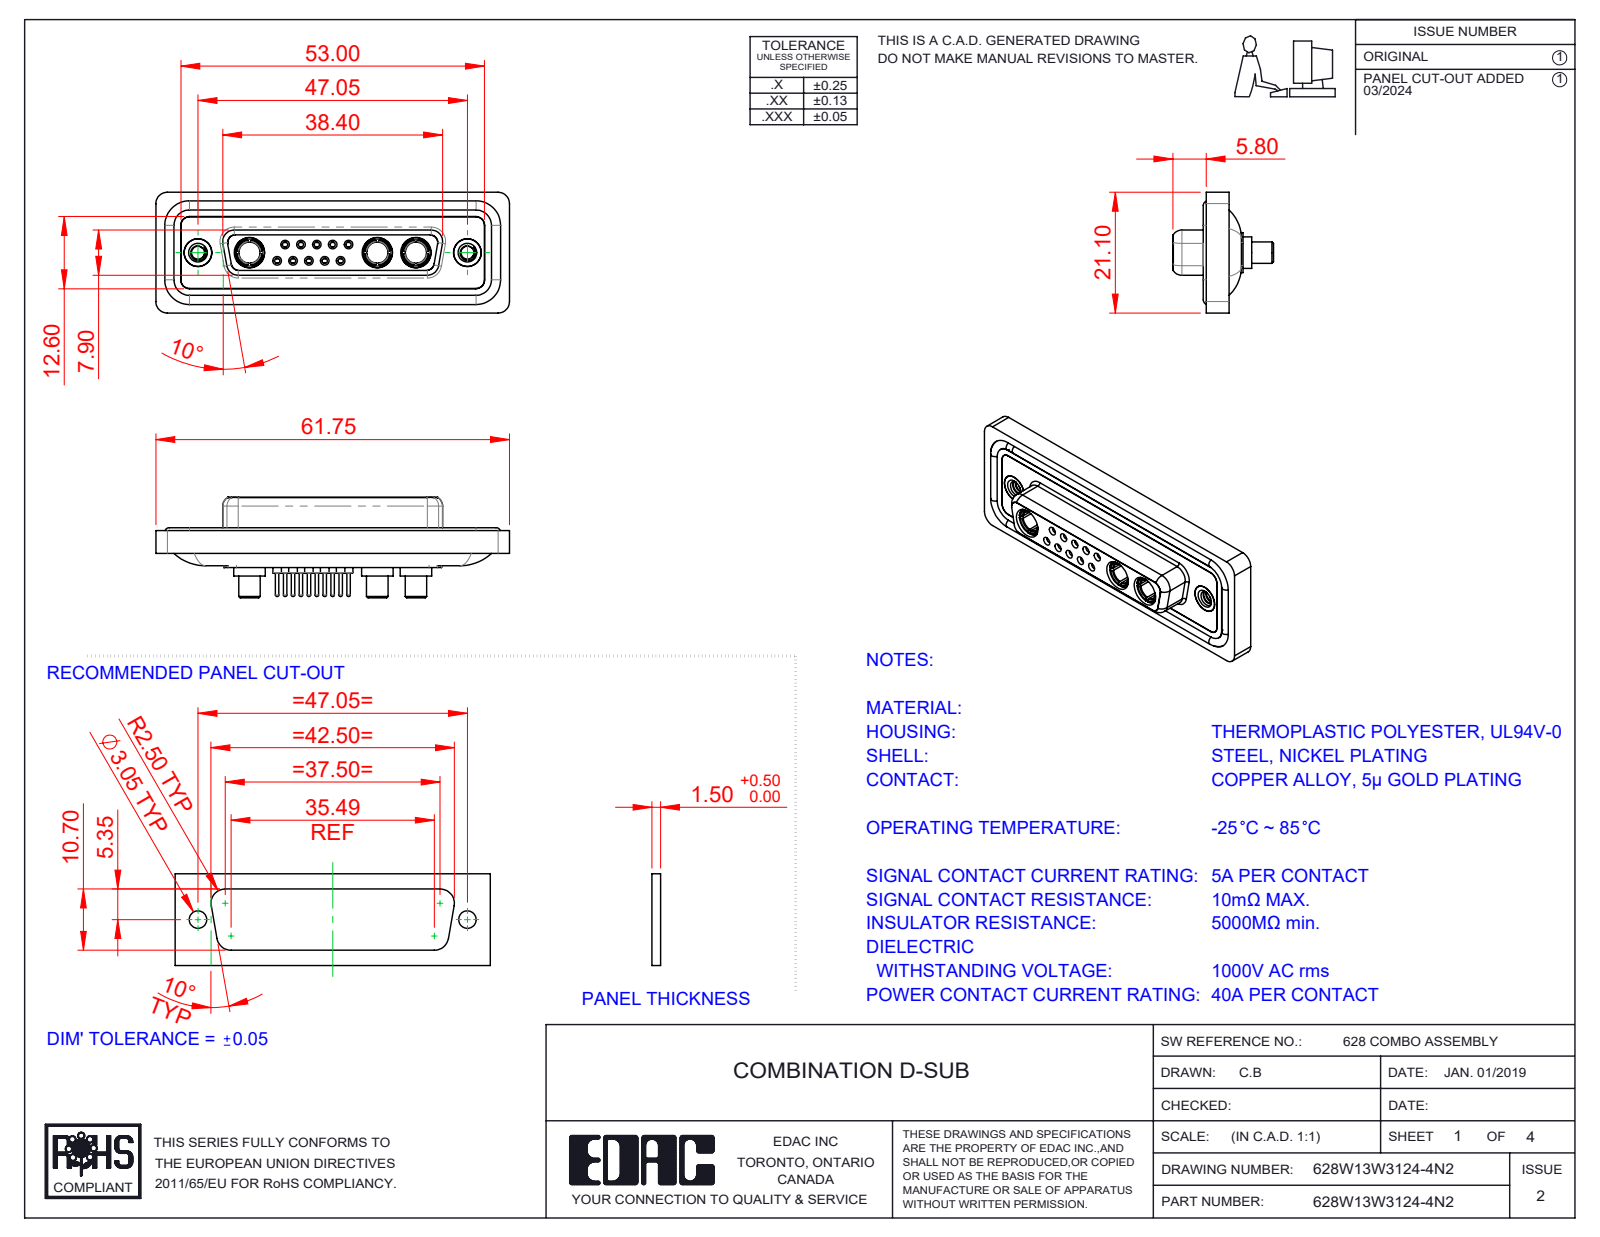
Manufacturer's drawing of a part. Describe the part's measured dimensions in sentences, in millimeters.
The part is named "628Combo Shell Rear_25 Contacts; 628Combo Waterproof Housing_25 Contacts; 628Combo Contact Row 1_24; Power Socket_40A S (+5 more)". Its 3-D file was written by "SolidWorks 2023 (CONFIG_CONTROL_DESIGN)". It is 23 solids with 1158 faces: 342 planar, 447 cylindrical and 369 other. Overall it measures 61.75 by 21.1 by 17.55 millimeters. Its volume is 8 329 cubic millimeters and its surface area 13 741 square millimeters. Round holes: 10 of diameter 0.9, 10 of diameter 1.1, 10 of diameter 1.5, 10 of diameter 2, 5 of diameter 1.6, 5 of diameter 1.7, 5 of diameter 4.85, 3 of diameter 3.7, 3 of diameter 5.3, 2 of diameter 2.26, 2 of diameter 4, 2 of diameter 4.05. Round bosses or shafts: 10 of diameter 2.2, 10 of diameter 0.6, 9 of diameter 1.6, 3 of diameter 5.5, 3 of diameter 5.2, 3 of diameter 4.96, 3 of diameter 4.75, 3 of diameter 3.75. Partial cylindrical surfaces (rounded edges, fillets, slot ends): 22 of radius 1.5, 18 of radius 2, 8 of radius 1.35, 8 of radius 1.6, 4 of radius 0.25, 4 of radius 0.5, 4 of radius 0.6, 4 of radius 0.65. The main face-to-face distances are 0.4, 1.8, 7.45, 5.65, 0.5, 6.6, 7.05, 1.6, 2.9, 1.1. The hole center spacings are 3.16, 2.77, 5.03, 5.04, 5.54, 8.31, 7.49, 2.76.
